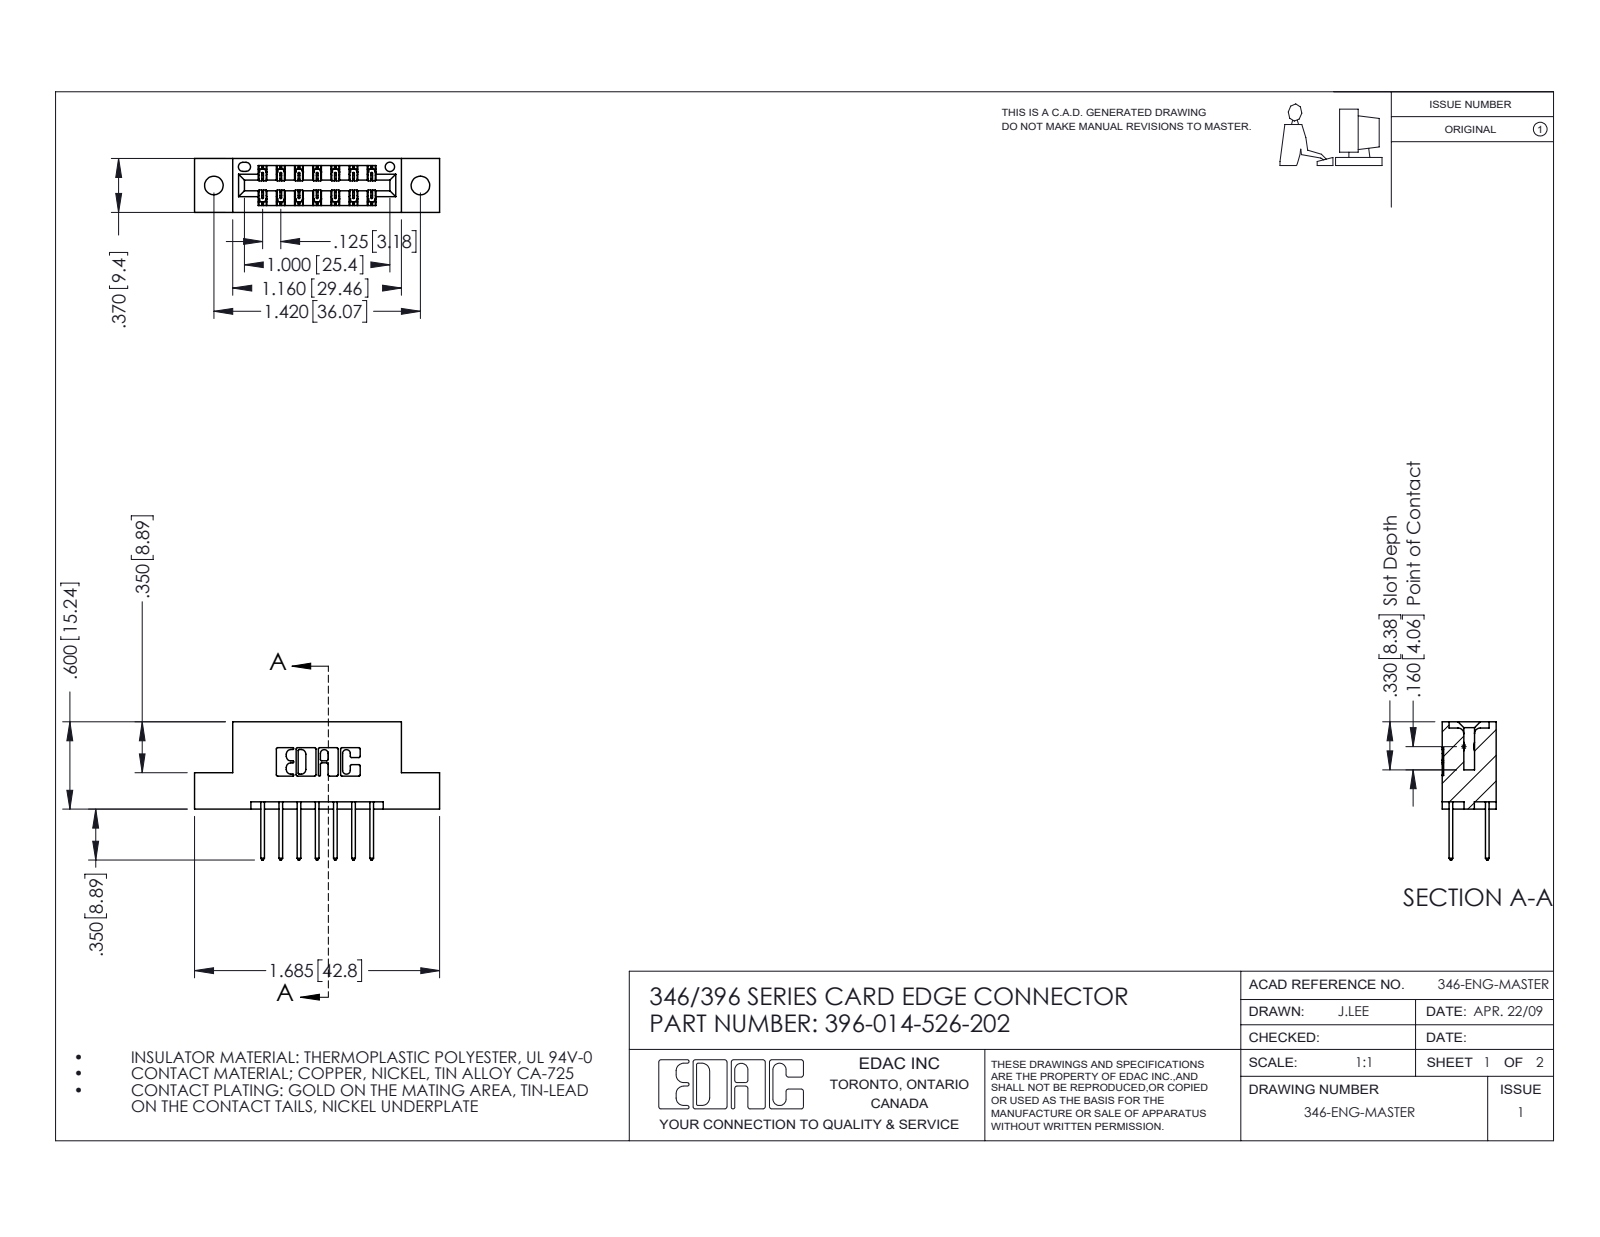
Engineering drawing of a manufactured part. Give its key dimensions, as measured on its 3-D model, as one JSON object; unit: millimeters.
{"part_name": "345-292-001_345-293-126; 396-014-526-202; 346 Part_Flush Mounting Lugs - 0.128 Dia", "step_written_by": "SolidWorks 2016 (CONFIG_CONTROL_DESIGN)", "units": "millimeters", "bodies": {"solids": 15, "faces": 850, "planar": 566, "cylindrical": 284, "other": 0}, "overall_size": [42.8, 24.1, 9.4], "volume_mm3": 3880, "surface_area_mm2": 4628, "round_holes": [[3.3, 2], [1.6, 1]], "partial_cylinders_radius": [[0.3, 22], [0.2, 21], [0.3, 14], [0.2, 6], [0.8, 6], [0.7, 3], [0.4, 2], [0.6, 2]], "face_to_face_distances": [6.4, 1.2, 8.2, 9.4, 1.8, 7.6, 0.6, 7, 3.8, 5.6], "hole_center_spacings": [6.2, 30.9, 36.1]}
